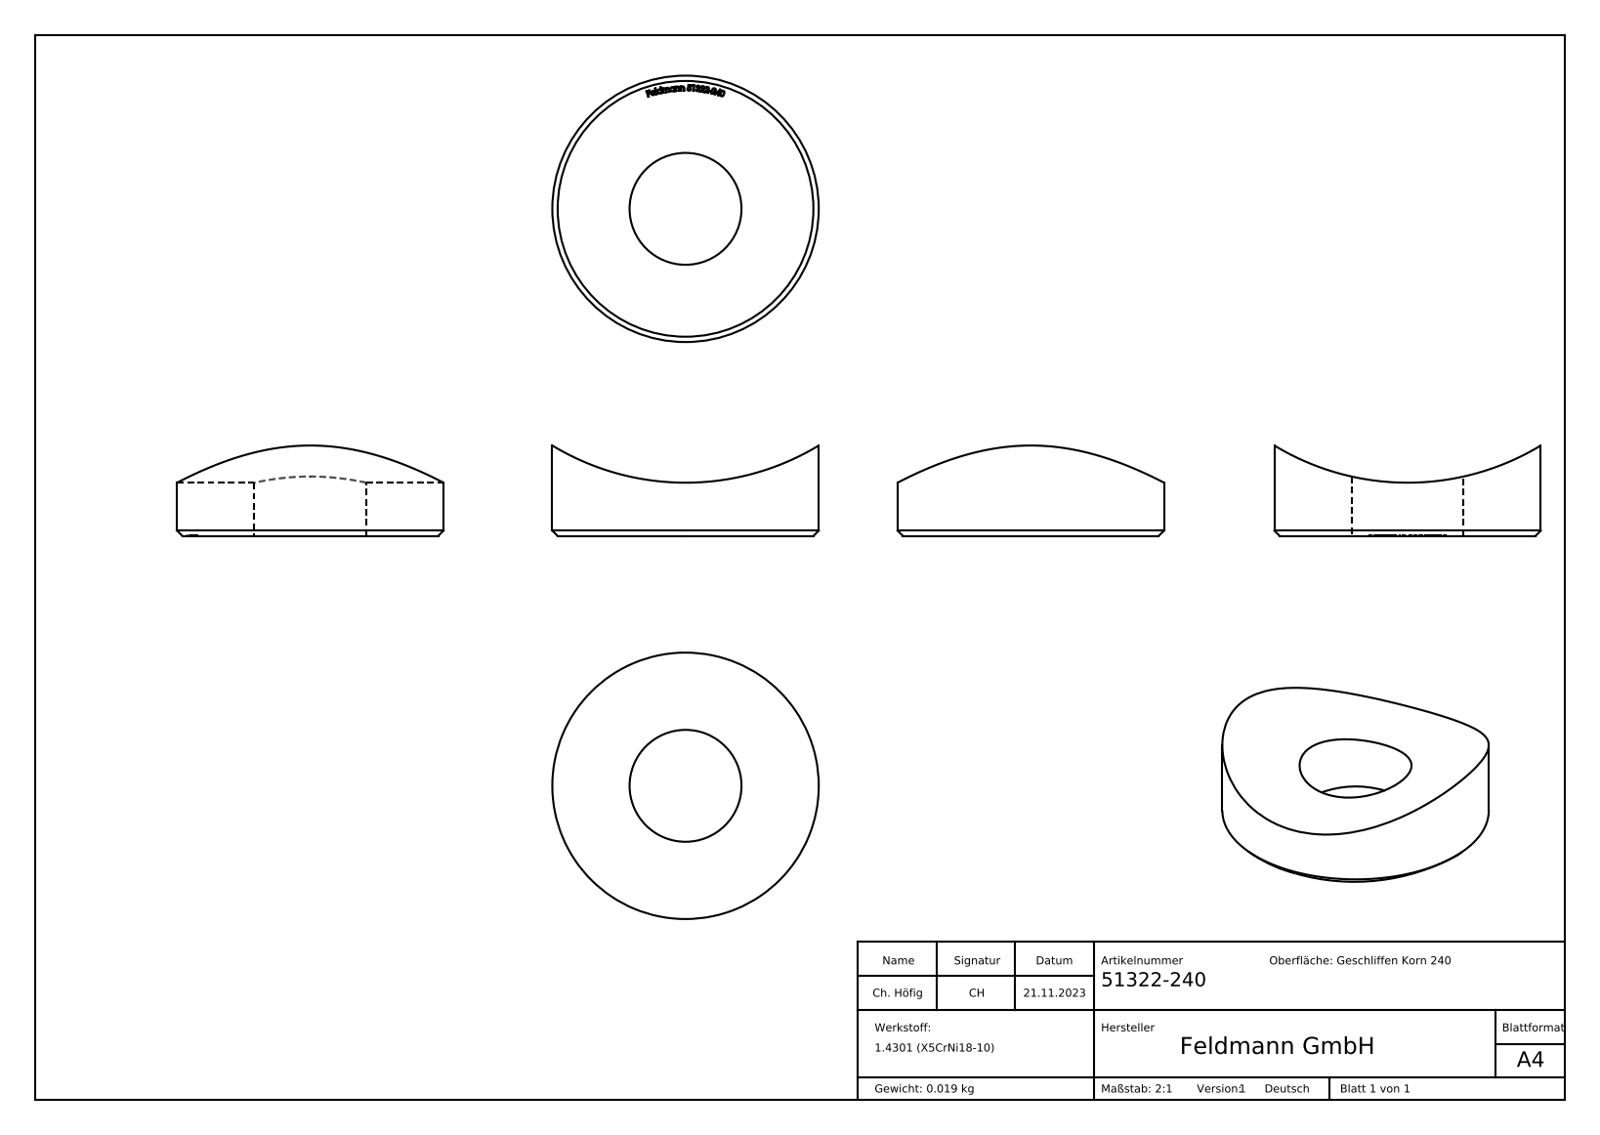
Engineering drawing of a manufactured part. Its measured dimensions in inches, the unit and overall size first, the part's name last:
Units: inches
Overall size (bounding box): 0.984 × 0.984 × 0.334
Round holes (diameter × count): ⌀0.413 ×1
Round bosses / shafts (diameter × count): ⌀0.984 ×1
Partial cylindrical surfaces — rounded edges, fillets, slot ends (radius × count): R0.951 ×1
Main face-to-face distances: 0.021, 0.013, 0.012, 0.023, 0.019, 0.015, 0.013, 0.014, 0.022
Volume: 0.147 in³ · Surface area: 2.337 in²
Bodies: 1 solid, 228 faces (127 planar, 3 cylindrical, 98 other)
Part name (STEP PRODUCT): 51322-240
STEP written by: SolidWorks 2018 (CONFIG_CONTROL_DESIGN)
